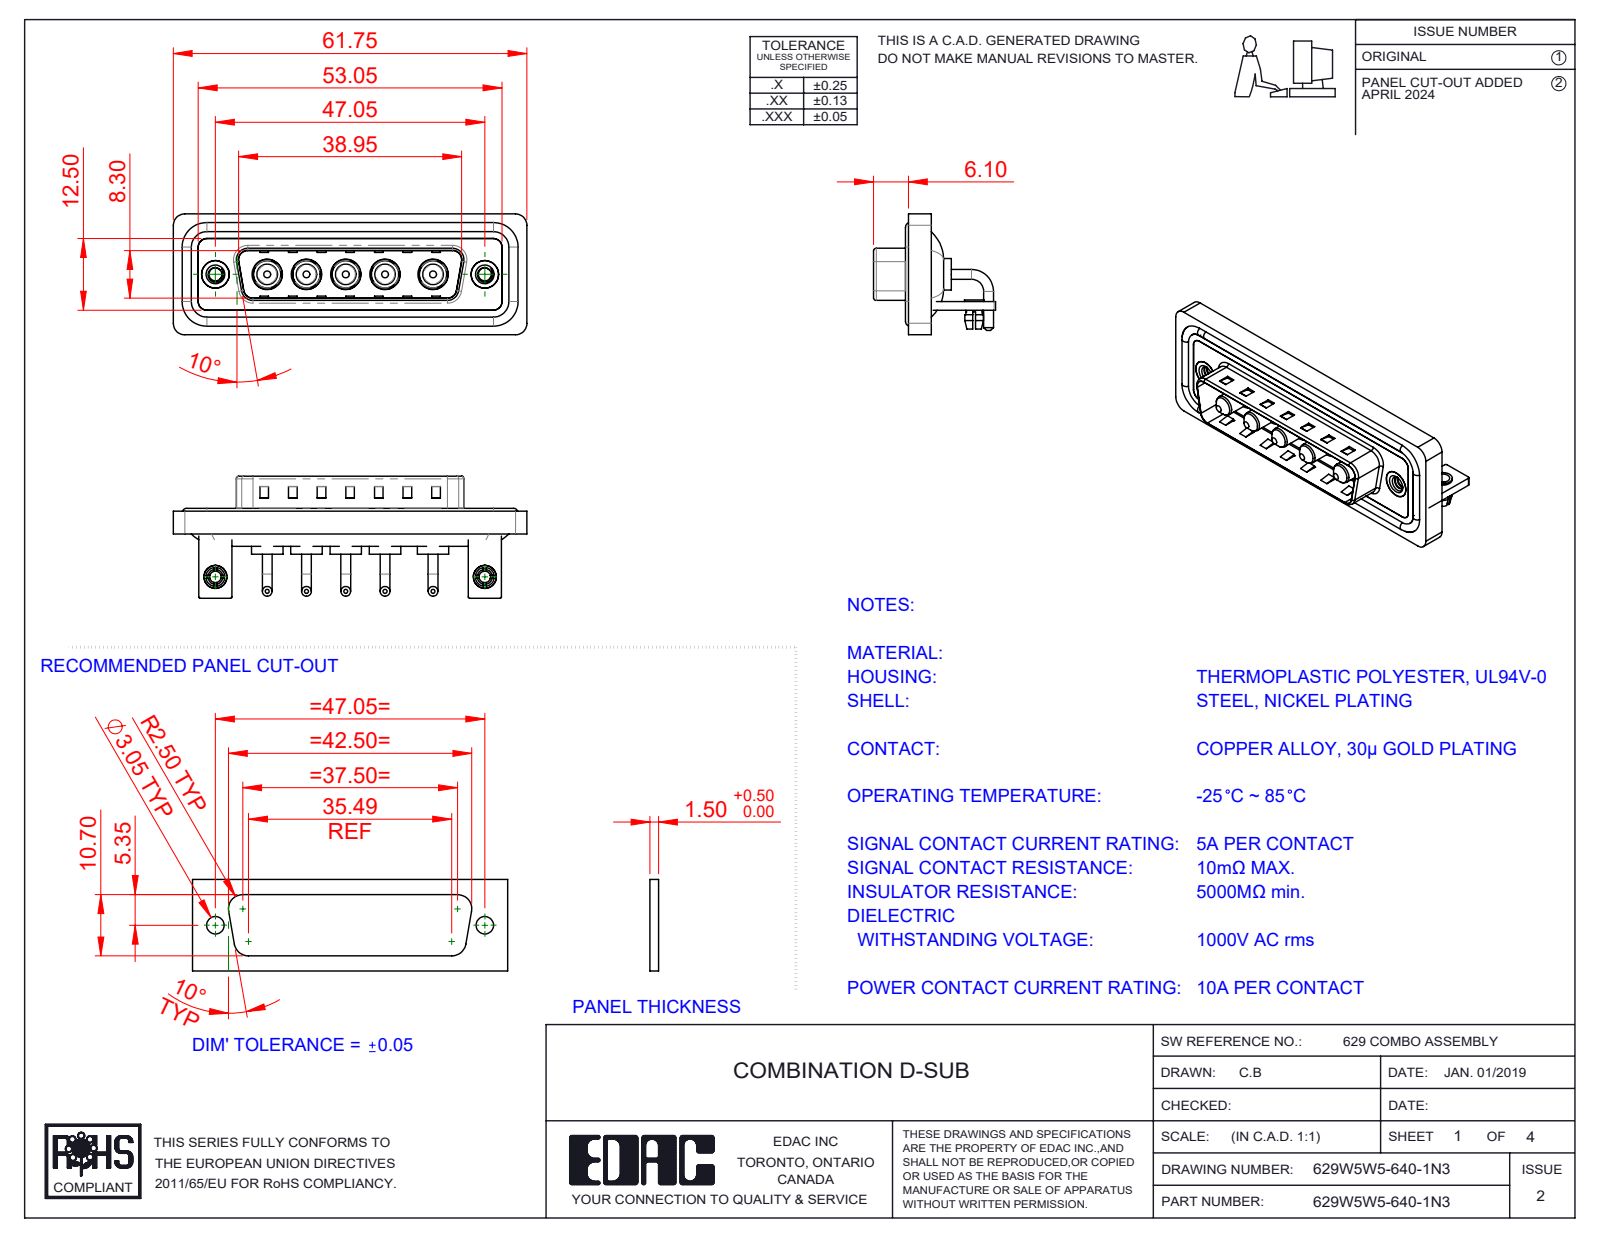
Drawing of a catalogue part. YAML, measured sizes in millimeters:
part_name: "629Combo Threaded Rivet_3; 629Combo Housing_5W5; 629Combo Shell Front_25 Contacts; 629Combo Stabilizer Bracket (+5 more)"
step_written_by: "SolidWorks 2023 (CONFIG_CONTROL_DESIGN)"
units: millimeters
bodies: {solids: 21, faces: 830, planar: 327, cylindrical: 343, other: 160}
overall_size: [61.75, 21.3, 21.1]
volume: 7826
surface_area: 12815
round_holes:
  - {diameter: 4.85, count: 5}
  - {diameter: 5.3, count: 5}
  - {diameter: 2, count: 2}
  - {diameter: 2.26, count: 2}
  - {diameter: 2.5, count: 2}
  - {diameter: 3.2, count: 2}
  - {diameter: 4, count: 2}
  - {diameter: 4.8, count: 2}
  - {diameter: 5, count: 2}
round_bosses_or_shafts:
  - {diameter: 1.7, count: 10}
  - {diameter: 5.5, count: 5}
  - {diameter: 5.2, count: 5}
  - {diameter: 4.75, count: 5}
  - {diameter: 3.75, count: 5}
  - {diameter: 3.6, count: 5}
  - {diameter: 1.6, count: 4}
  - {diameter: 4.9, count: 2}
partial_cylinders:
  - {radius: 2, count: 19}
  - {radius: 1.5, count: 18}
  - {radius: 0.25, count: 16}
  - {radius: 0.5, count: 9}
  - {radius: 1.6, count: 8}
  - {radius: 2.1, count: 5}
  - {radius: 0.6, count: 4}
  - {radius: 0.65, count: 4}
face_to_face_distances: [0.4, 1.5, 2.9, 0.8, 2.1, 1.1, 3.7, 4.5, 4.1, 1.2]
hole_center_spacings: [6.86, 13.73, 47.05, 6.85, 6.87, 8.37, 8.38, 9.04]
